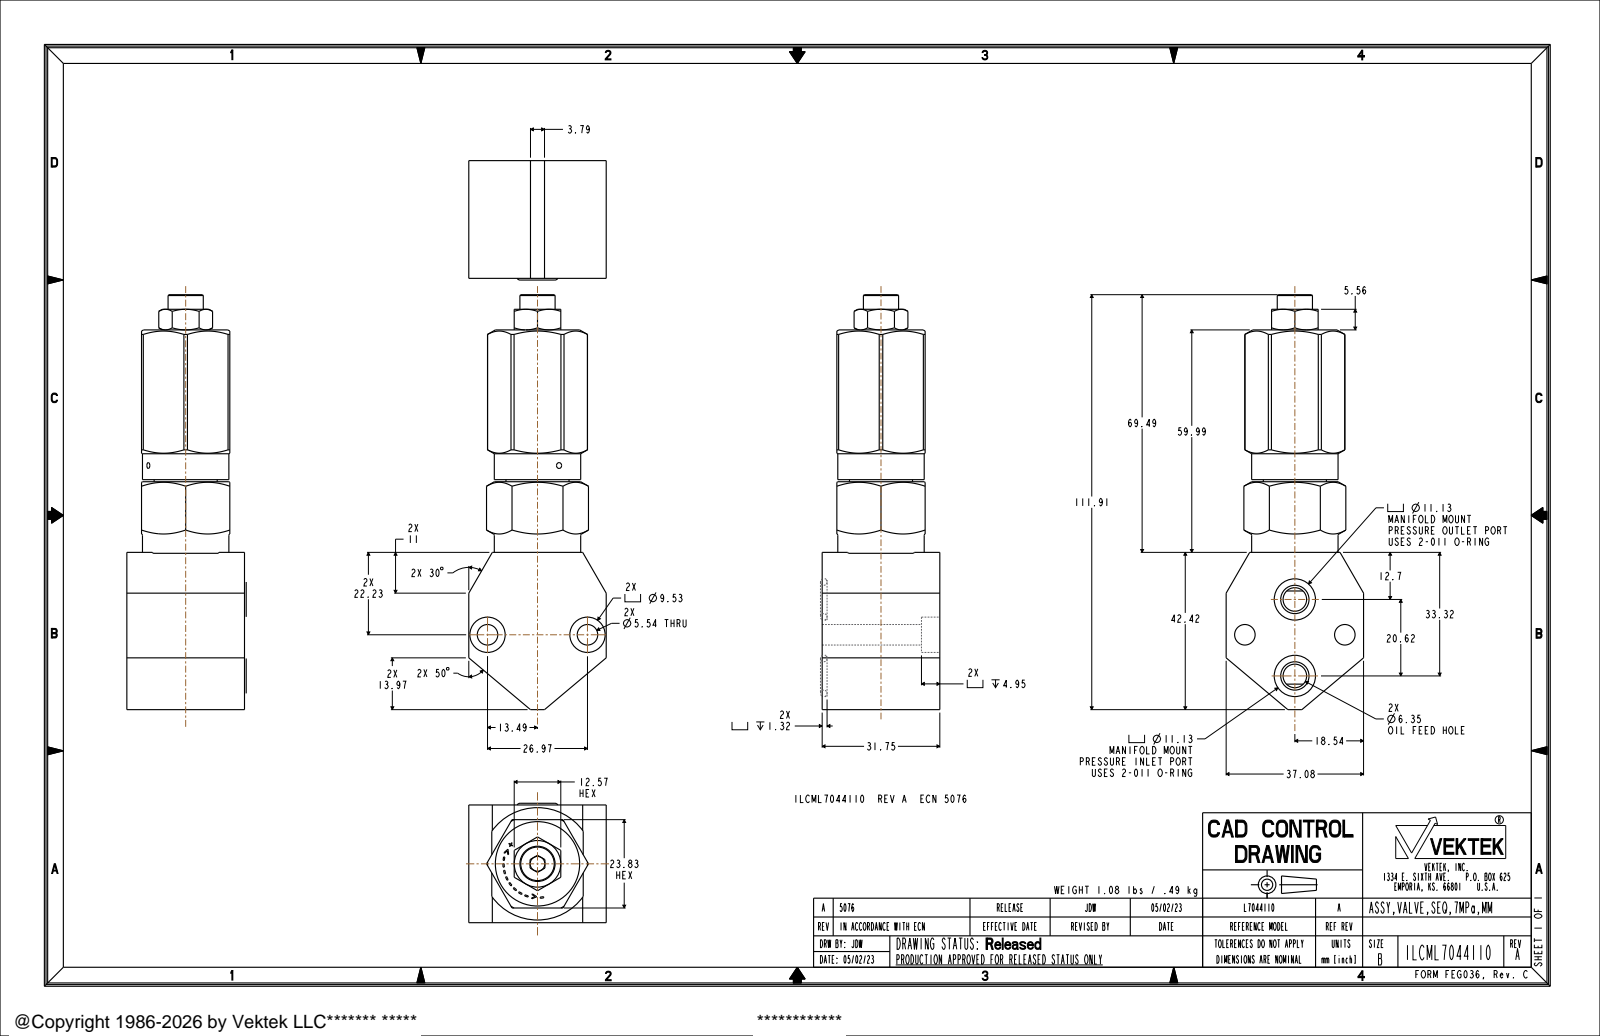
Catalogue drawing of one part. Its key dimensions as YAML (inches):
part_name: "ILCML7044110"
step_written_by: "CREO PARAMETRIC BY PTC INC, 2021164 (AUTOMOTIVE_DESIGN)"
units: inches
bodies: {solids: 1, faces: 222, planar: 122, cylindrical: 54, other: 46}
overall_size: [4.406, 1.46, 1.268]
volume: 2.818
surface_area: 31.36
round_holes:
  - {diameter: 0.218, count: 2}
  - {diameter: 0.25, count: 2}
  - {diameter: 0.375, count: 2}
  - {diameter: 0.438, count: 2}
  - {diameter: 0.062, count: 1}
  - {diameter: 0.157, count: 1}
  - {diameter: 0.66, count: 1}
  - {diameter: 0.685, count: 1}
  - {diameter: 0.734, count: 1}
round_bosses_or_shafts:
  - {diameter: 0.918, count: 1}
  - {diameter: 0.67, count: 1}
  - {diameter: 0.374, count: 1}
partial_cylinders:
  - {radius: 0.531, count: 1}
  - {radius: 0.596, count: 1}
face_to_face_distances: [0.938, 0.156, 1.094, 1.25, 1.46, 2.372, 0.119, 2.253, 1.59, 1.471]
hole_center_spacings: [0.65, 0.688, 0.812, 1.062]
